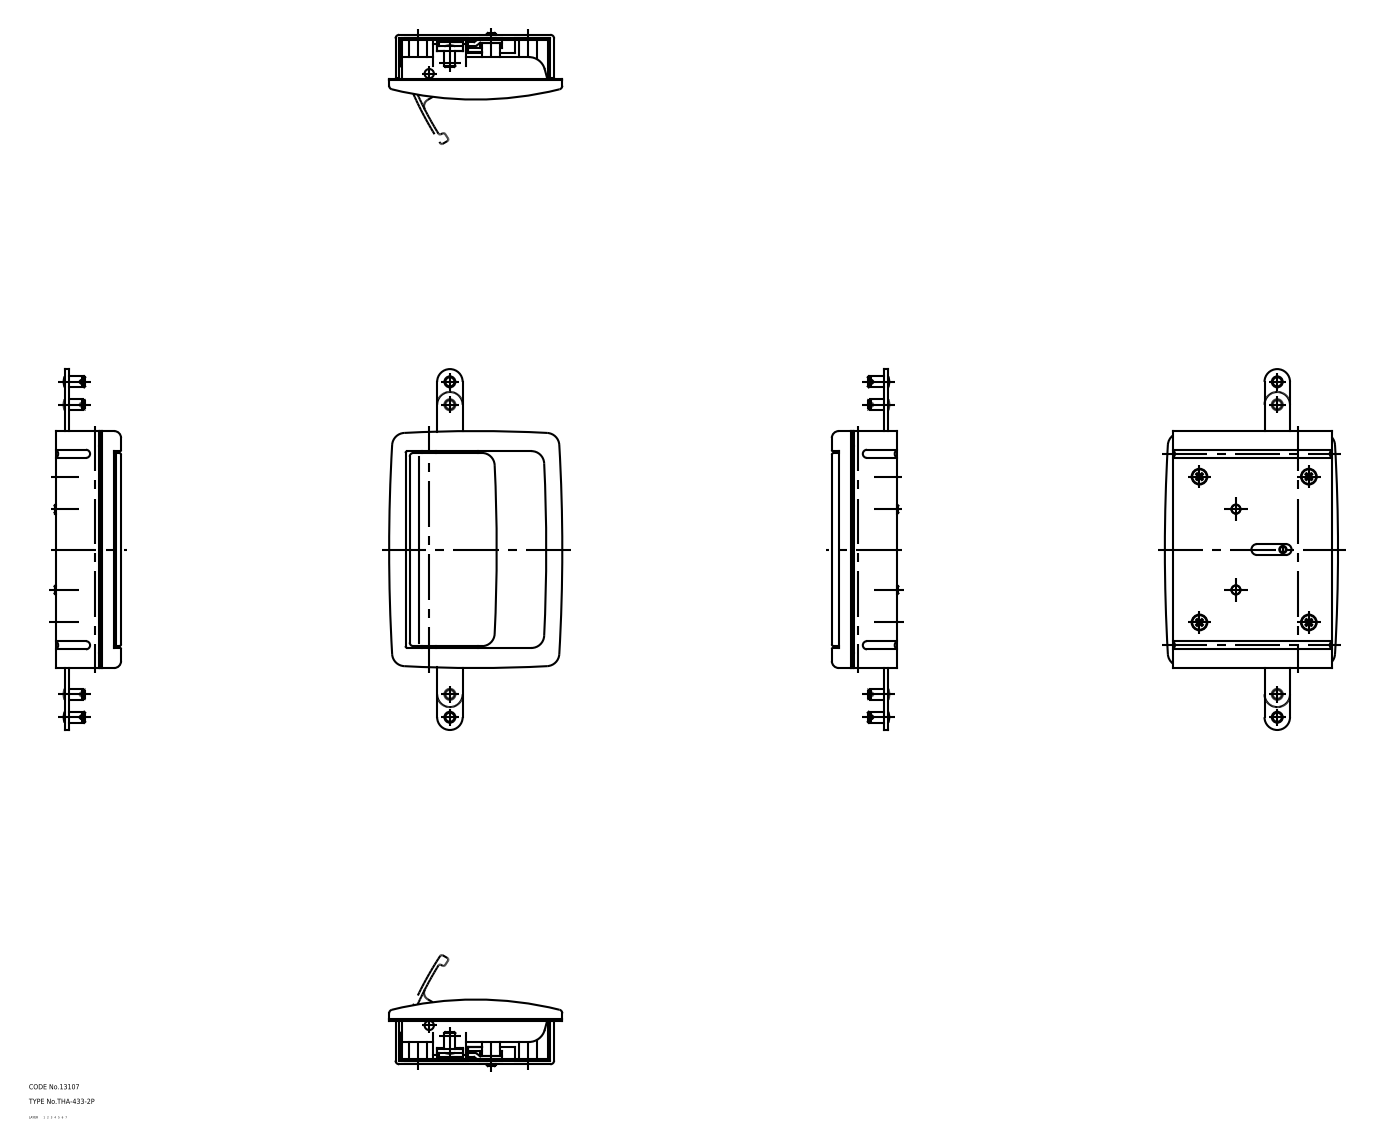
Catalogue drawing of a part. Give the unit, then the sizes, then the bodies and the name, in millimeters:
Units: millimetres
Overall size (bounding box): 198 × 95 × 36.5
Volume: 136 063 mm³ · Surface area: 112 660 mm²
Bodies: 14 solids, 582 faces (0 planar, 0 cylindrical, 582 other)
Part name (STEP PRODUCT): link_B; link_C_mr; pin_mr; pin_1_mr (+8 more)
STEP written by: CADfix (AUTOMOTIVE_DESIGN)
